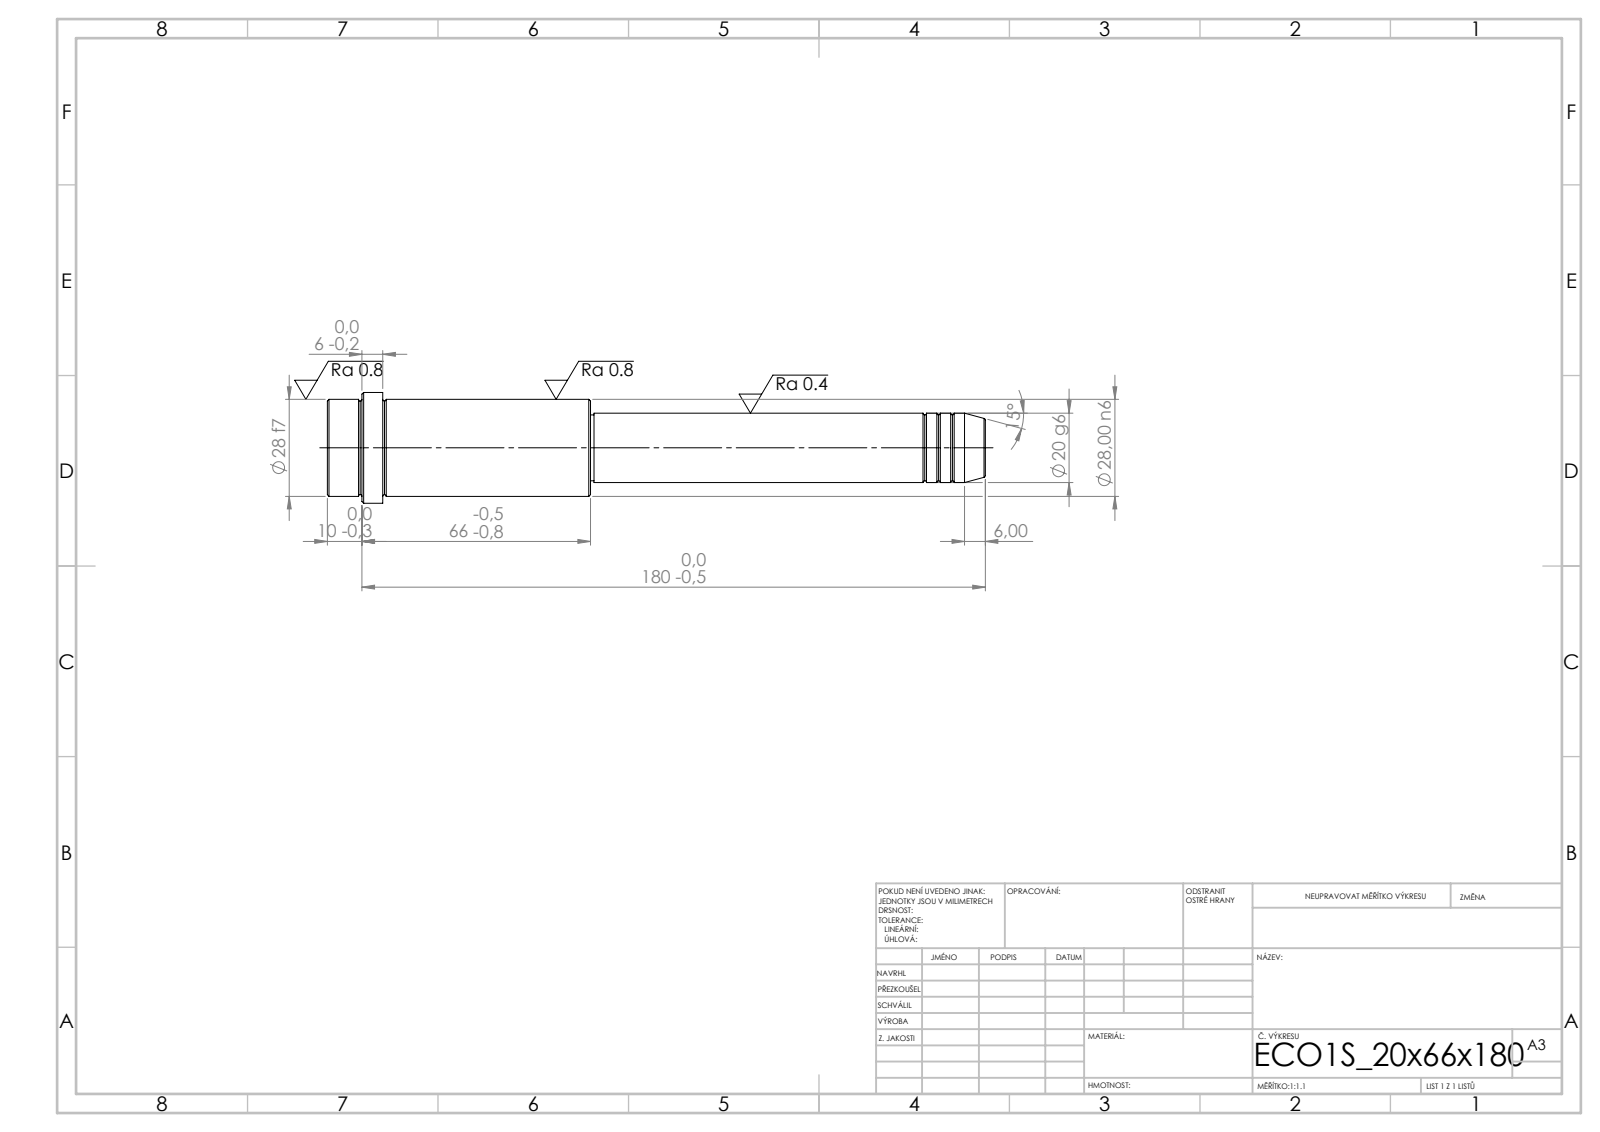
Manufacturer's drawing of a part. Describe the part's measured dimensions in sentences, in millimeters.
Its 3-D file was written by "SolidWorks 2019 (CONFIG_CONTROL_DESIGN)". It is 1 solid with 52 faces: 6 planar, 16 cylindrical and 30 other. Overall it measures 190 by 32 by 32 millimeters. Its volume is 83 249 cubic millimeters and its surface area 15 584 square millimeters. Round bosses or shafts: 1 of diameter 32, 1 of diameter 28, 1 of diameter 20, 1 of diameter 19. The main face-to-face distances are 76, 114, 190, 174, 60, 16, 180, 66, 6, 10.
